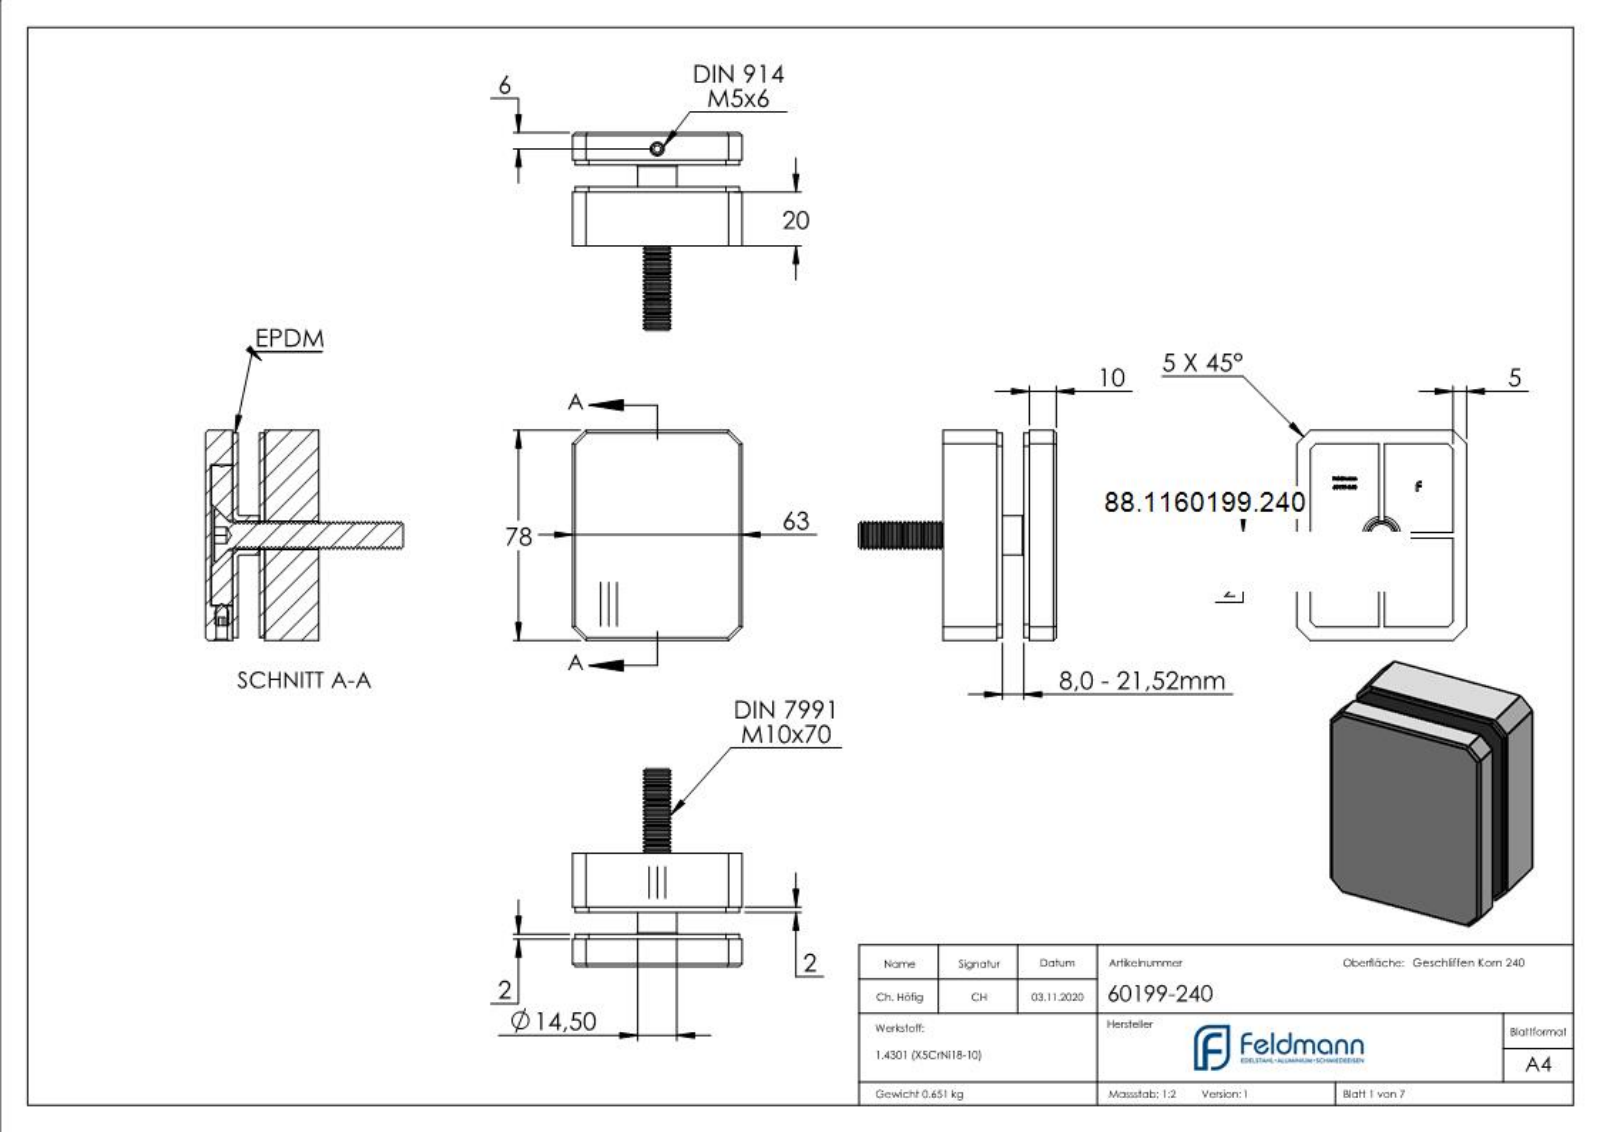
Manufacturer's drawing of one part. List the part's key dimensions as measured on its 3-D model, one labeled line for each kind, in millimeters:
Part name (STEP PRODUCT): socket countersunk head screw_din_DIN 7991 - M10 x 70 --- 70S; socket set screw cone point_din; 60199-240 Teil3; socket set screw cone point_din_DIN 914 - M5 x 8-S (+8 more)
STEP written by: SolidWorks 2018 (CONFIG_CONTROL_DESIGN)
Units: millimetres
Bodies: 7 solids, 803 faces (253 planar, 180 cylindrical, 370 other)
Overall size (bounding box): 78 × 73.36 × 63
Volume: 102 914 mm³ · Surface area: 69 002 mm²
Round holes (diameter × count): ⌀4.2 ×1, ⌀5 ×1, ⌀10.5 ×1, ⌀11 ×1, ⌀22.73 ×1, ⌀52.5 ×1
Round bosses / shafts (diameter × count): ⌀56.5 ×1, ⌀52 ×1, ⌀19.48 ×1, ⌀14.5 ×1, ⌀14 ×1, ⌀10 ×1, ⌀5 ×1
Partial cylindrical surfaces — rounded edges, fillets, slot ends (radius × count): R0.2 ×40
Main face-to-face distances: 10, 2, 12, 20, 8, 5, 22, 15, 18, 17
